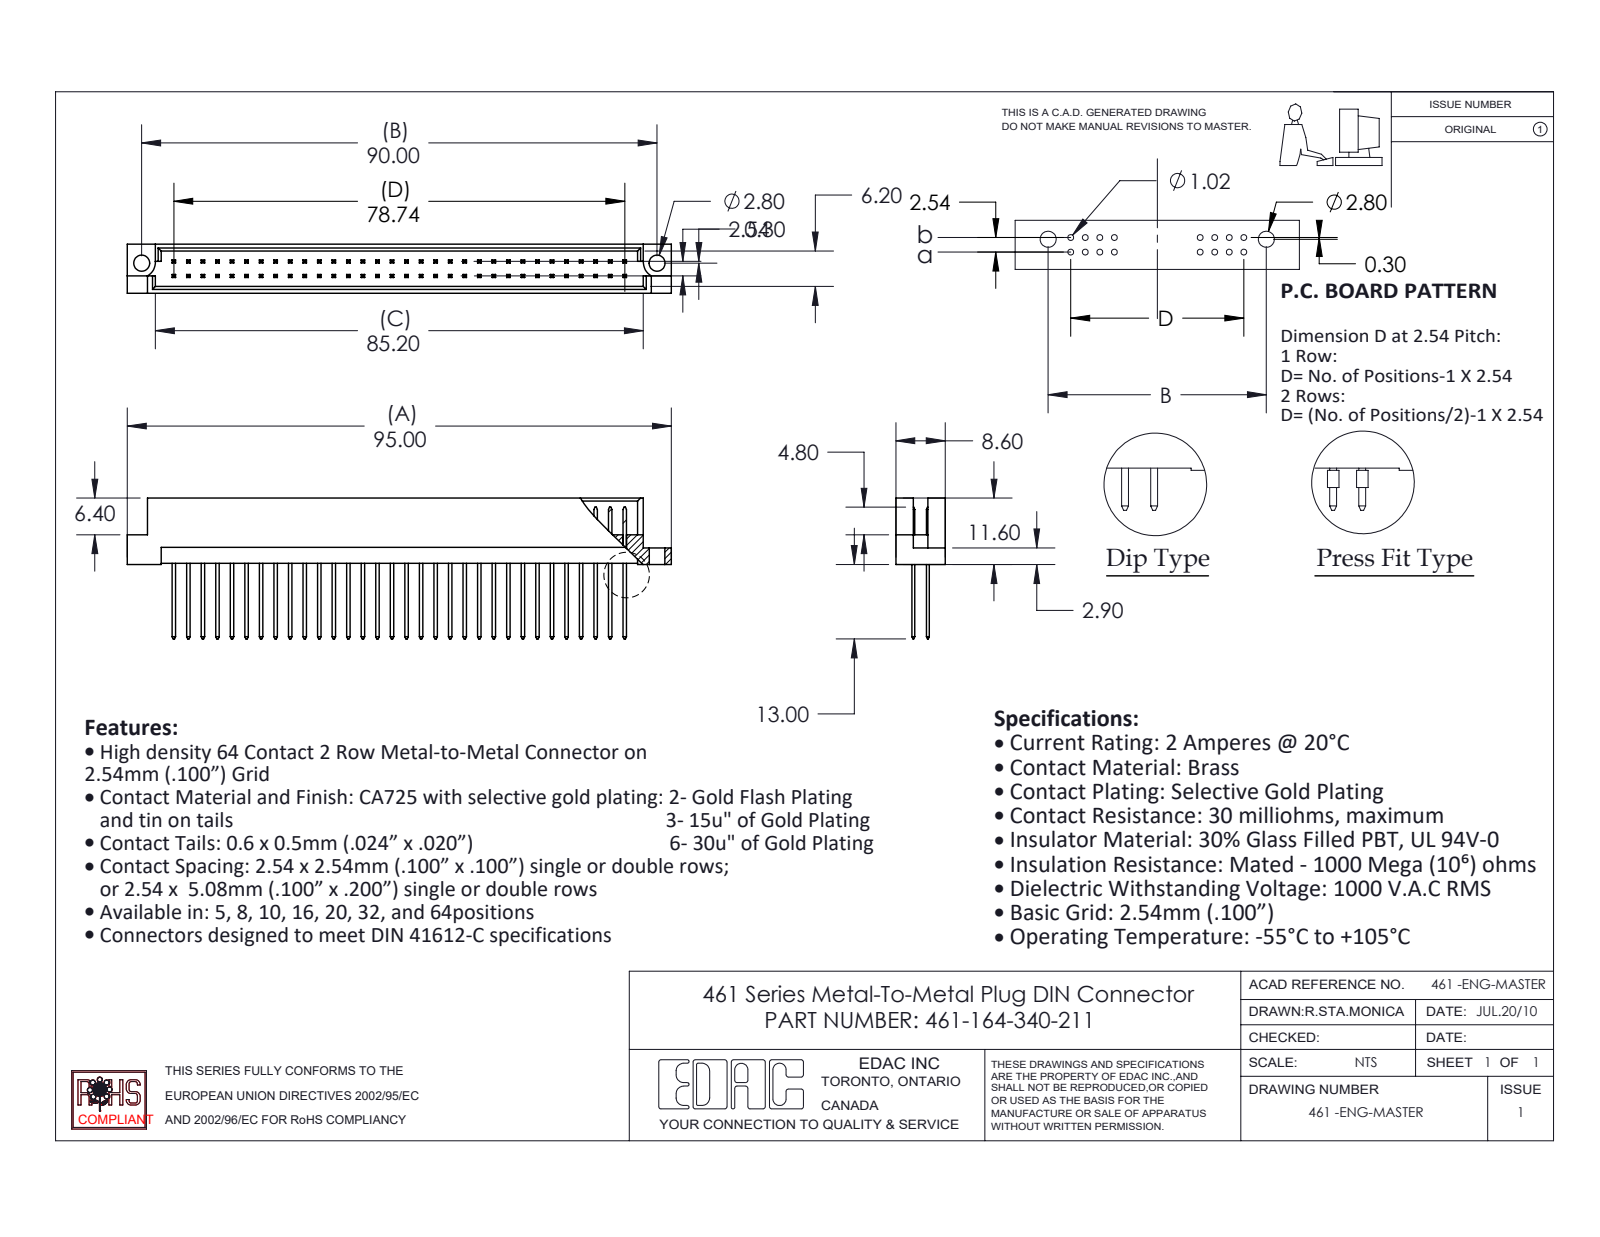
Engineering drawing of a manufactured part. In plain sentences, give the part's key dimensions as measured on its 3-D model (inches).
The part is named "461-164-340-211; 461 Part_64; 461-290_40". Its 3-D file was written by "SolidWorks 2020 (CONFIG_CONTROL_DESIGN)". It is 65 solids with 1201 faces: 1194 planar, 7 cylindrical and 0 other. Overall it measures 3.74 by 0.969 by 0.339 inches. Its volume is 0.311 cubic inches and its surface area 13.77 square inches. Round holes: 2 of diameter 0.11. Partial cylindrical surfaces (rounded edges, fillets, slot ends): 2 of radius 0.11. The main face-to-face distances are 0.1, 0.047, 0.291, 0.109, 0.129, 0.209, 0.229, 0.062, 0.082, 0.162. The hole center spacings are 3.543.
